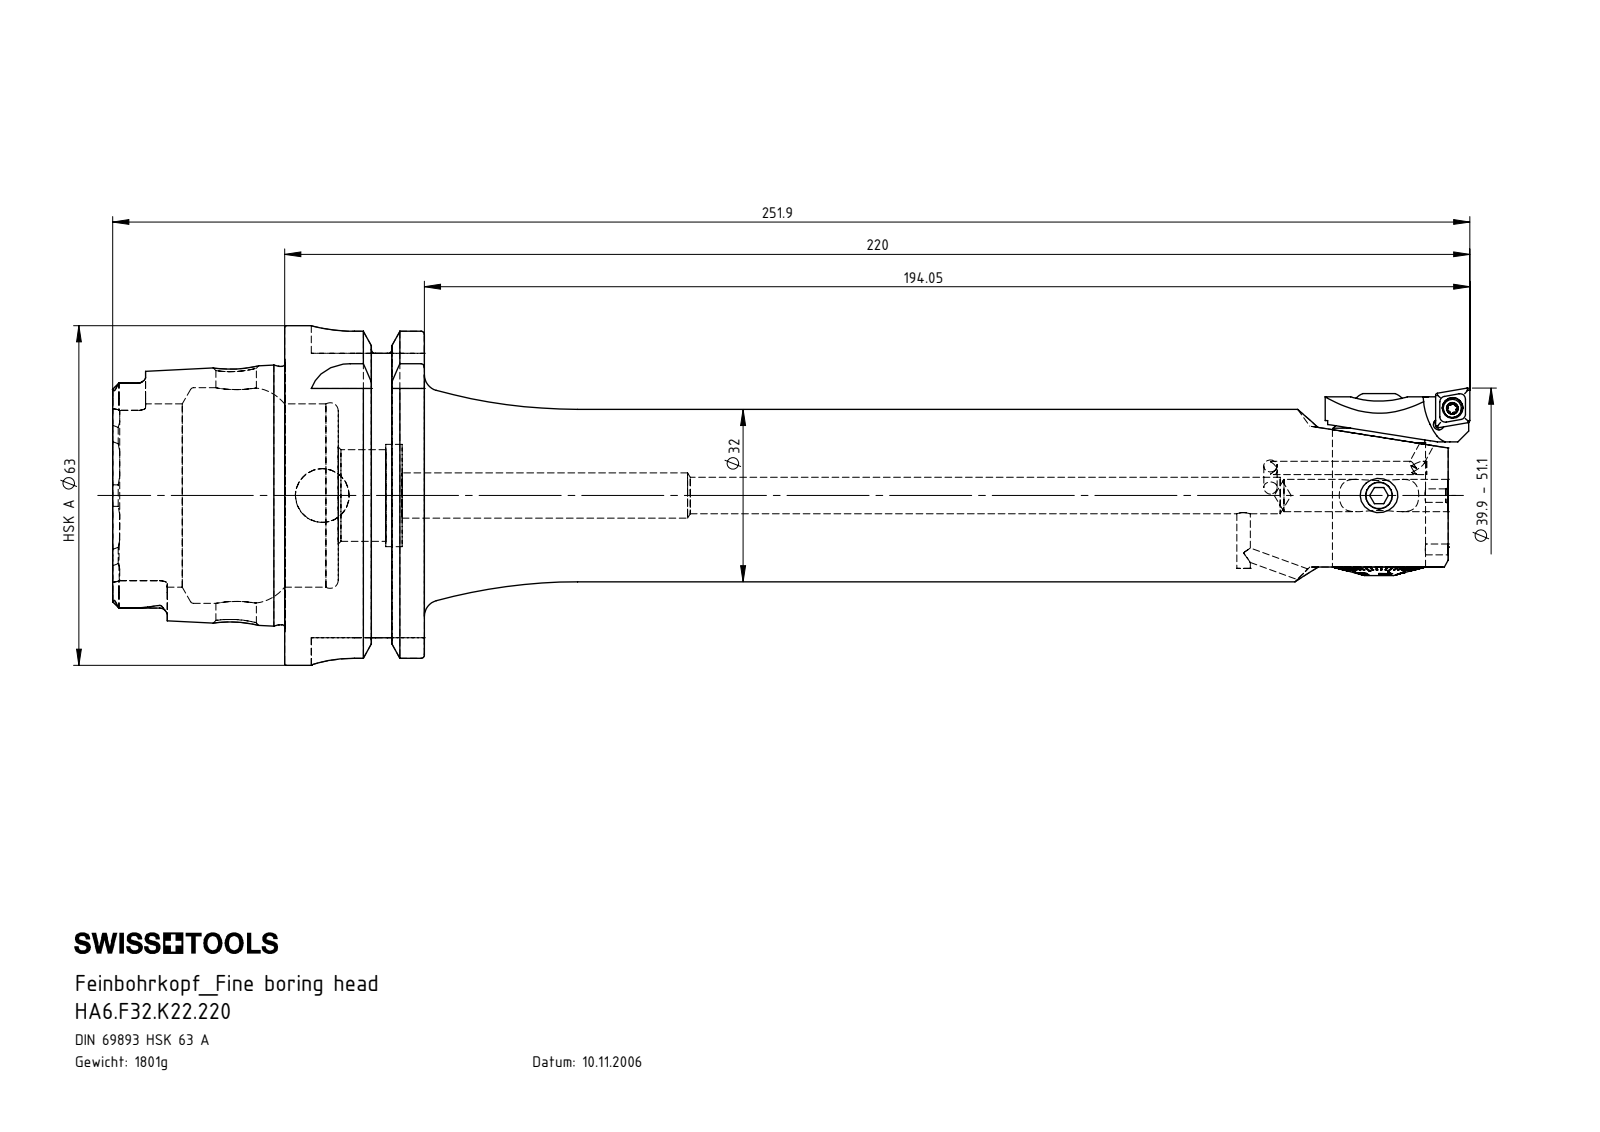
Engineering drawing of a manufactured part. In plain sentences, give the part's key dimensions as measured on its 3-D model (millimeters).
The part is named "F32-ER1.101.010_A; WCA-ER2.001.006_A; F32-BG1.002.017_B; HA6-F32.K20.220_B_Fertigbearbeitung (+8 more)". Its 3-D file was written by "SolidWorks 2022 (CONFIG_CONTROL_DESIGN)". It is 13 solids with 851 faces: 342 planar, 172 cylindrical and 337 other. Overall it measures 251.9 by 63 by 63 millimeters. Its volume is 228 907 cubic millimeters and its surface area 53 085 square millimeters. Round holes: 5 of diameter 2.5, 2 of diameter 5, 2 of diameter 17, 1 of diameter 2, 1 of diameter 2.05, 1 of diameter 2.1, 1 of diameter 2.7, 1 of diameter 2.8, 1 of diameter 2.9, 1 of diameter 3, 1 of diameter 3.85, 1 of diameter 6. Round bosses or shafts: 2 of diameter 10, 1 of diameter 63, 1 of diameter 54.95, 1 of diameter 47.94, 1 of diameter 32, 1 of diameter 17, 1 of diameter 16.98, 1 of diameter 16.85. Partial cylindrical surfaces (rounded edges, fillets, slot ends): 6 of radius 0.21, 6 of radius 1.4, 4 of radius 0.36, 4 of radius 0.5, 4 of radius 2.88, 4 of radius 8, 2 of radius 0.36, 2 of radius 1.75. The main face-to-face distances are 25.95, 16, 9.95, 206.05, 216, 190.05, 31.9, 41.85, 57.85, 247.9. The hole center spacings are 3.84, 4, 5.6, 5.7, 8, 9.85, 10.61, 11.68.
